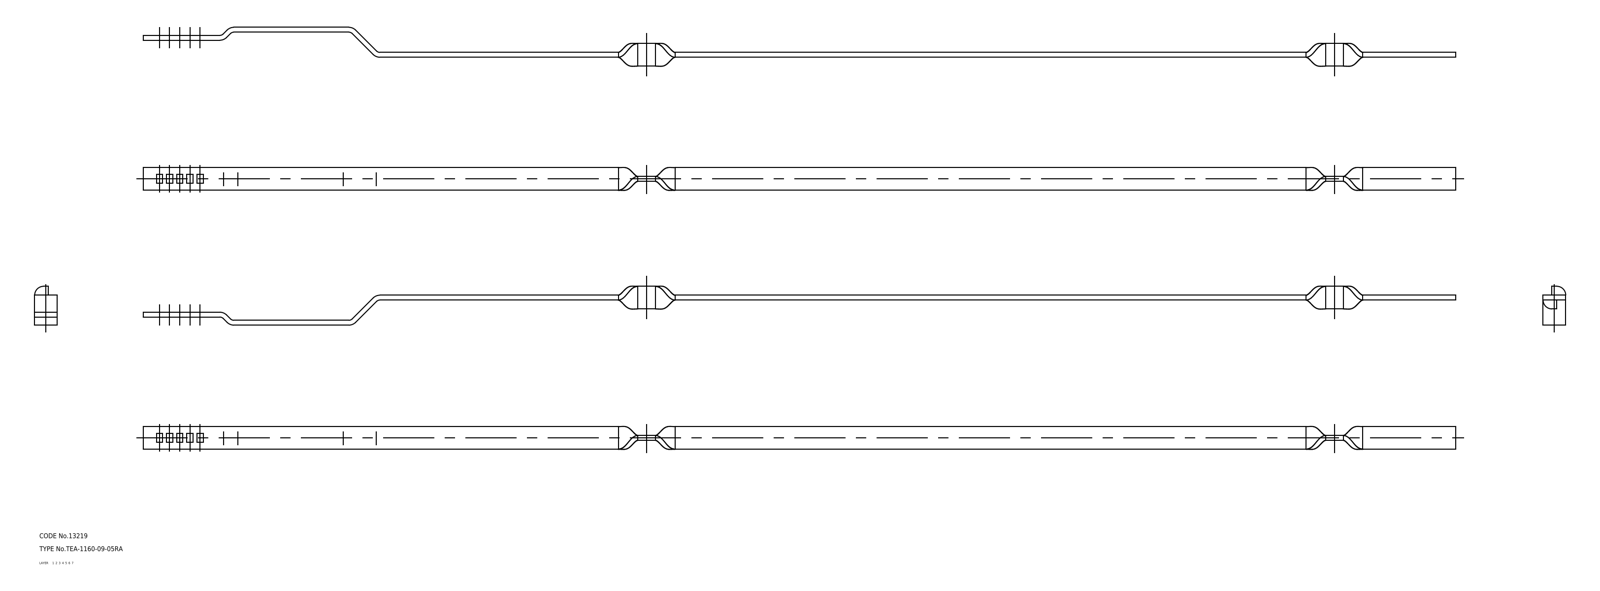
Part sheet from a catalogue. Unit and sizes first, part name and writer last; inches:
Units: inches
Overall size (bounding box): 31.929 × 0.946 × 0.572
Volume: 2.079 in³ · Surface area: 43.64 in²
Bodies: 1 solid, 74 faces (0 planar, 0 cylindrical, 74 other)
Part name (STEP PRODUCT): rod
STEP written by: CADfix (AUTOMOTIVE_DESIGN)
